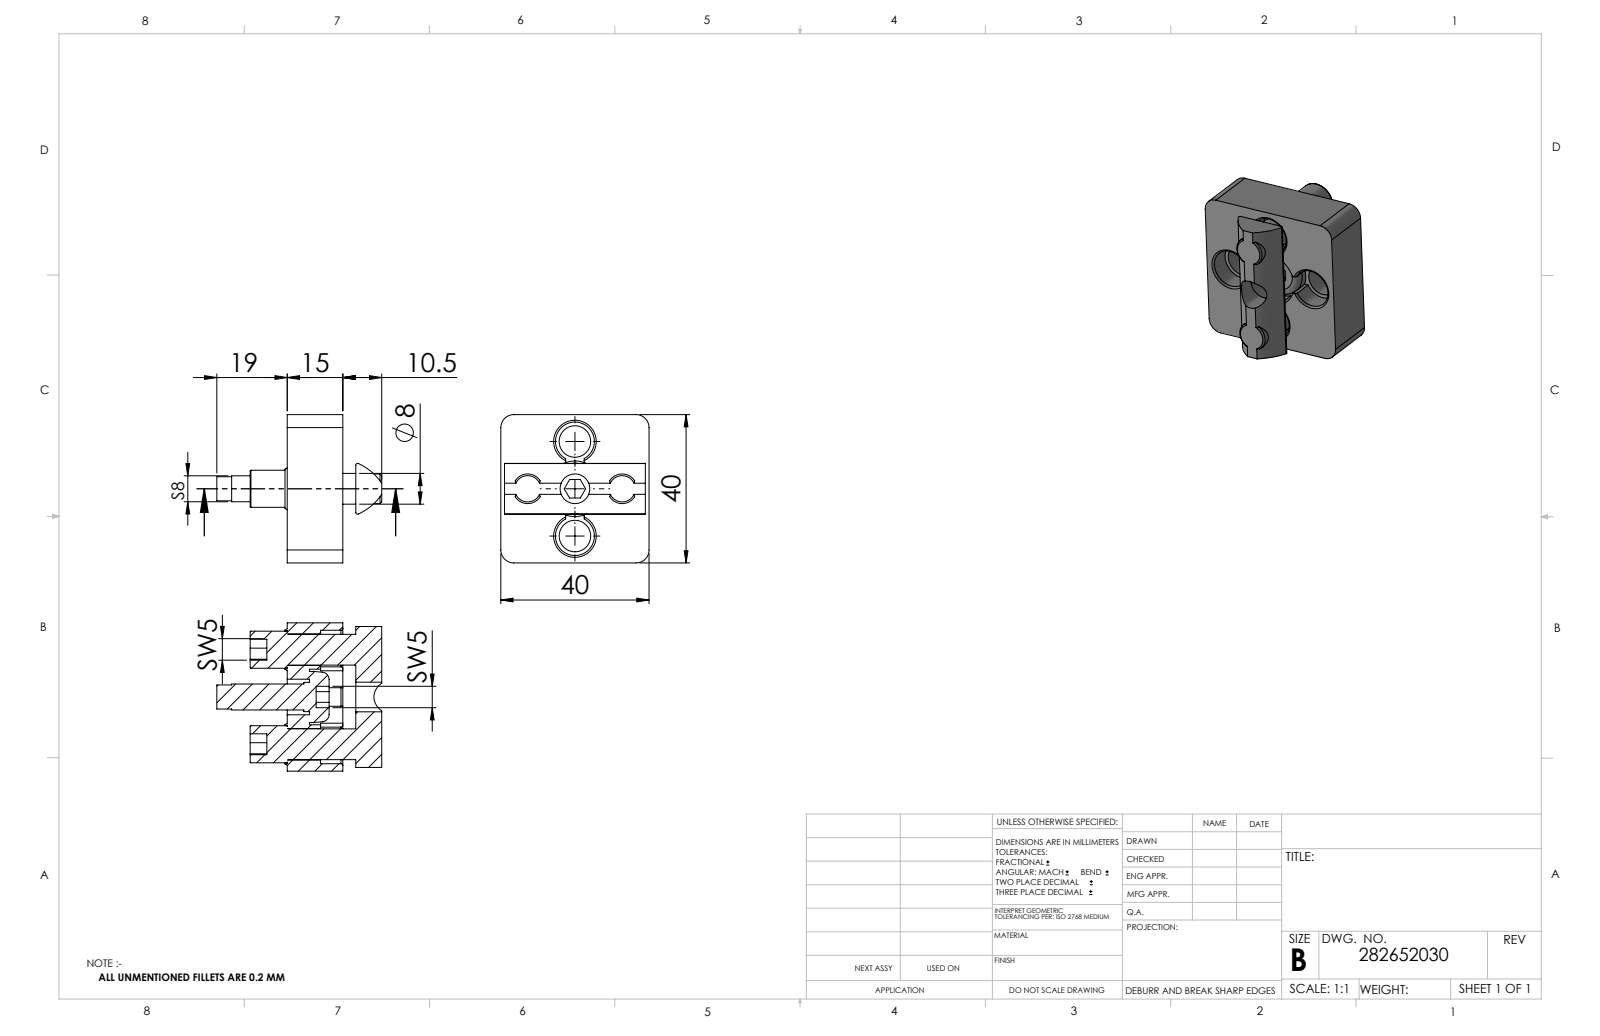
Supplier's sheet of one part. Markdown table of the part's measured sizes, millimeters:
| quantity | value |
| --- | --- |
| part name | 282652030_c_1 |
| STEP written by | SolidWorks 2014 (CONFIG_CONTROL_DESIGN) |
| units | millimeters |
| bodies | 1 solid, 176 faces (76 planar, 68 cylindrical, 32 other) |
| overall size | 44.5 × 40 × 40 |
| volume | 20 230 mm³ |
| surface area | 13 138 mm² |
| round holes (diameter × count) | 8.5 × 4, 10.5 × 4, 10.3 × 2, 8 × 1, 9.6 × 1, 15 × 1 |
| round bosses / shafts (diameter × count) | 10 × 2, 8.3 × 2, 13.8 × 1, 7.9 × 1, 7 × 1, 6.5 × 1 |
| partial cylindrical surfaces (radius × count) | 0.5 × 18, 3.5 × 4, 4 × 2, 15 × 2 |
| main face-to-face distances | 40, 10, 24, 3, 13, 27, 37, 15, 34, 14 |
| hole center spacings | 12.75, 18.03, 25.5 |
